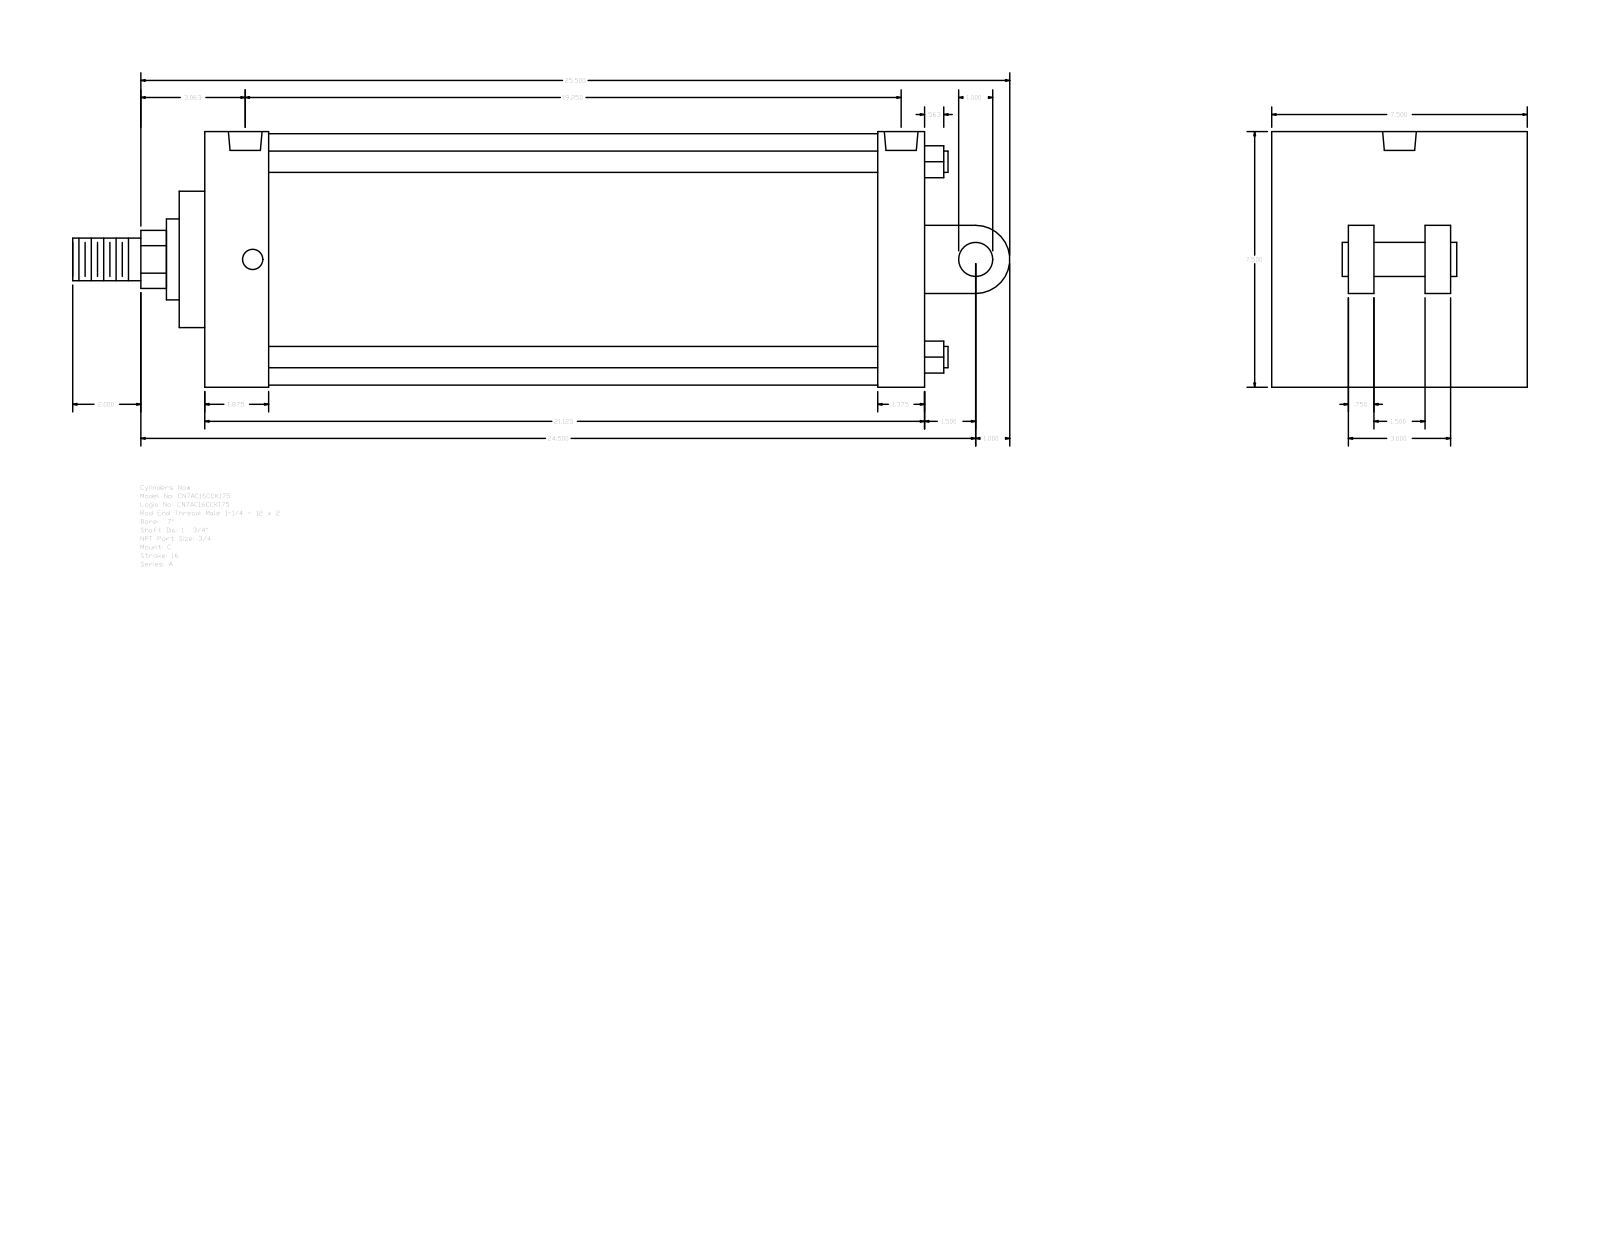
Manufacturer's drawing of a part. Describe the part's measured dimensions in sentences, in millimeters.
The part is named "A_C__0700_1.75". Its 3-D file was written by "GSSL Pune (CONFIG_CONTROL_DESIGN)". It is 0 solids with 104 faces: 75 planar, 29 cylindrical and 0 other. Overall it measures 698.5 by 190.5 by 190.5 millimeters. Round holes: 4 of diameter 15.08, 2 of diameter 25.12. Round bosses or shafts: 4 of diameter 15.88, 1 of diameter 187.32, 1 of diameter 60.33, 1 of diameter 44.45, 1 of diameter 31.75, 1 of diameter 25.4. Partial cylindrical surfaces (rounded edges, fillets, slot ends): 1 of radius 21.63, 1 of radius 25.4. The main face-to-face distances are 190.5, 536.58, 19.05, 76.2, 57.15, 146.05, 44.45, 69.85, 47.63, 488.95. The hole center spacings are 5.56, 477.83, 483.39, 488.95.
